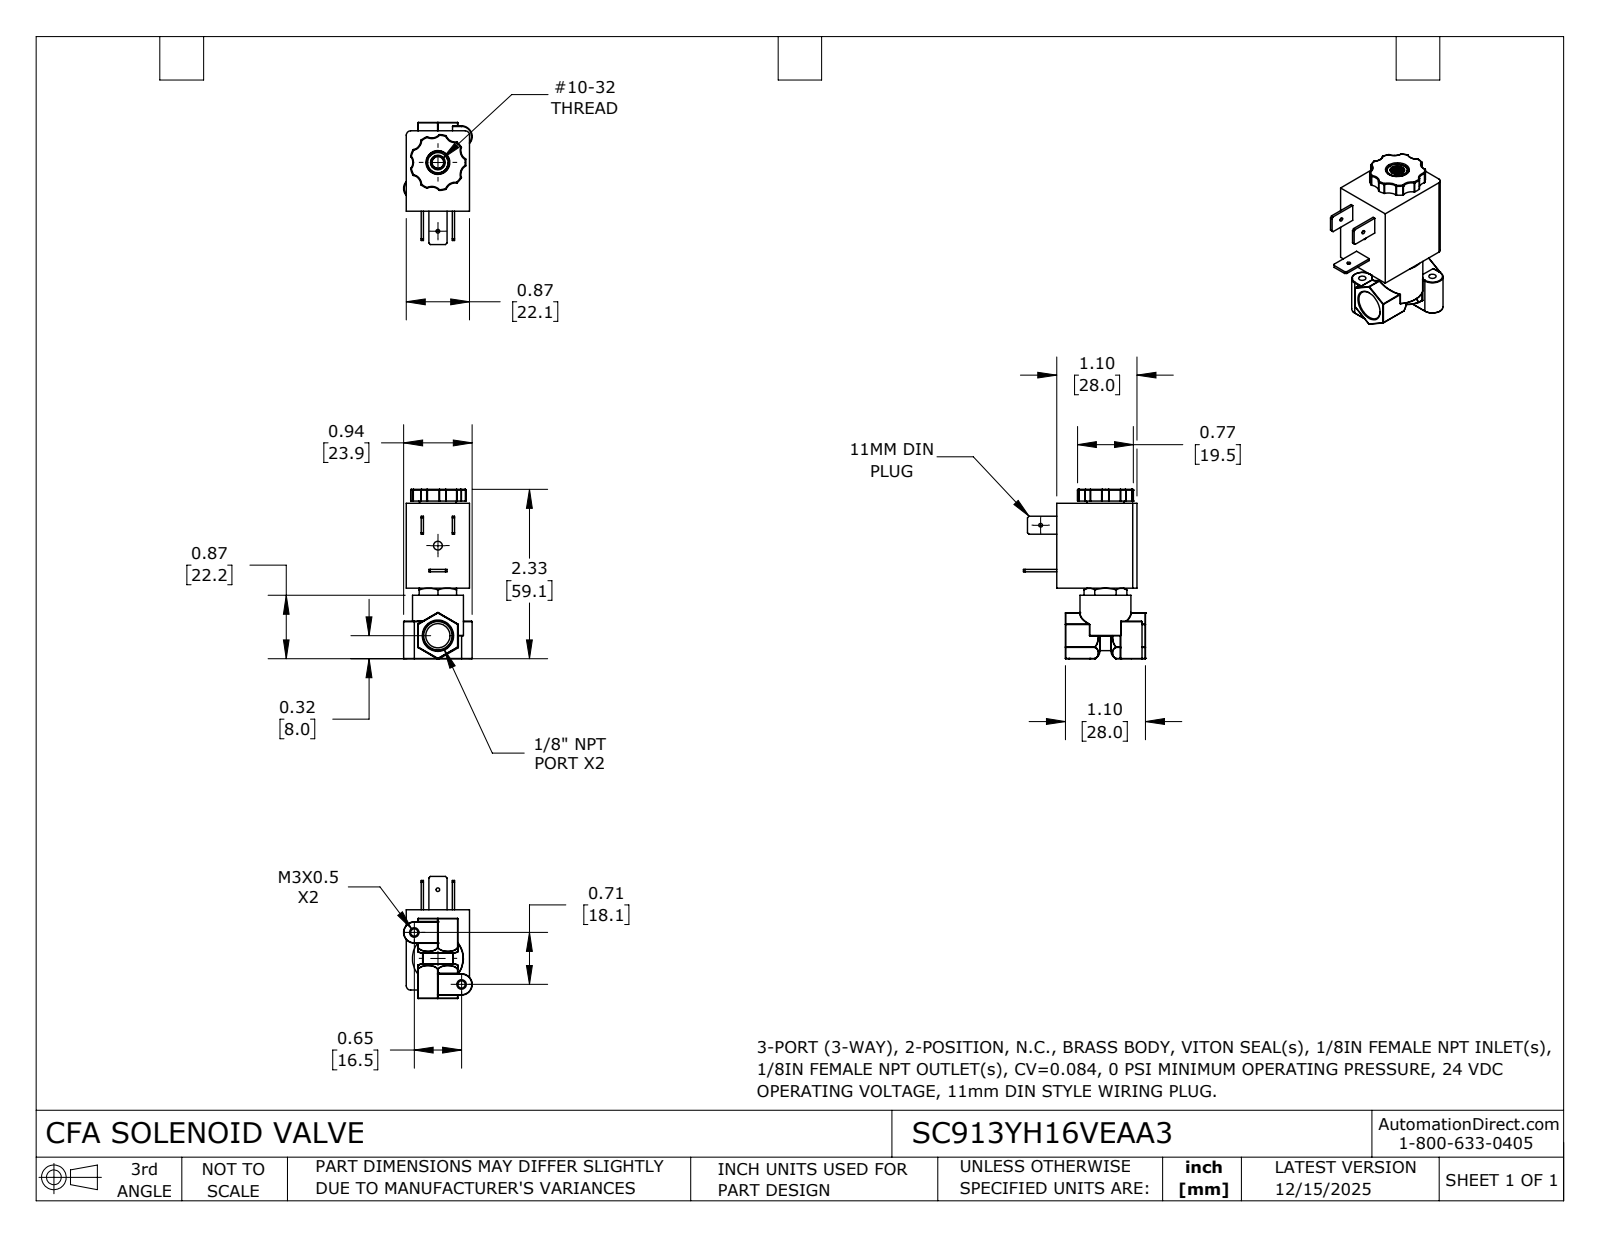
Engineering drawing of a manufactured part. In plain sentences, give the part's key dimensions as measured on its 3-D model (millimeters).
The part is named "SC913YH16VEAA3". Its 3-D file was written by "SolidWorks 2024 (CONFIG_CONTROL_DESIGN)". It is 1 solid with 363 faces: 70 planar, 142 cylindrical and 151 other. Overall it measures 59.1 by 42.6 by 23.9 millimeters. Its volume is 25 780 cubic millimeters and its surface area 8 955 square millimeters. Round holes: 2 of diameter 1.3, 2 of diameter 2.5, 1 of diameter 3, 1 of diameter 4.1, 1 of diameter 8.3, 1 of diameter 8.4. Round bosses or shafts: 1 of diameter 17.8, 1 of diameter 8. Partial cylindrical surfaces (rounded edges, fillets, slot ends): 29 of radius 0.1, 18 of radius 0.3, 12 of radius 0.2, 7 of radius 3.4, 2 of radius 0.4, 2 of radius 1.5, 2 of radius 3.4, 2 of radius 3.7. The main face-to-face distances are 22.1, 28, 29.6, 13.9, 34.5, 4.8, 4.1, 18, 24.7, 54.3. The hole center spacings are 12.3, 17.1, 24, 24.5, 31.4, 34.1.
